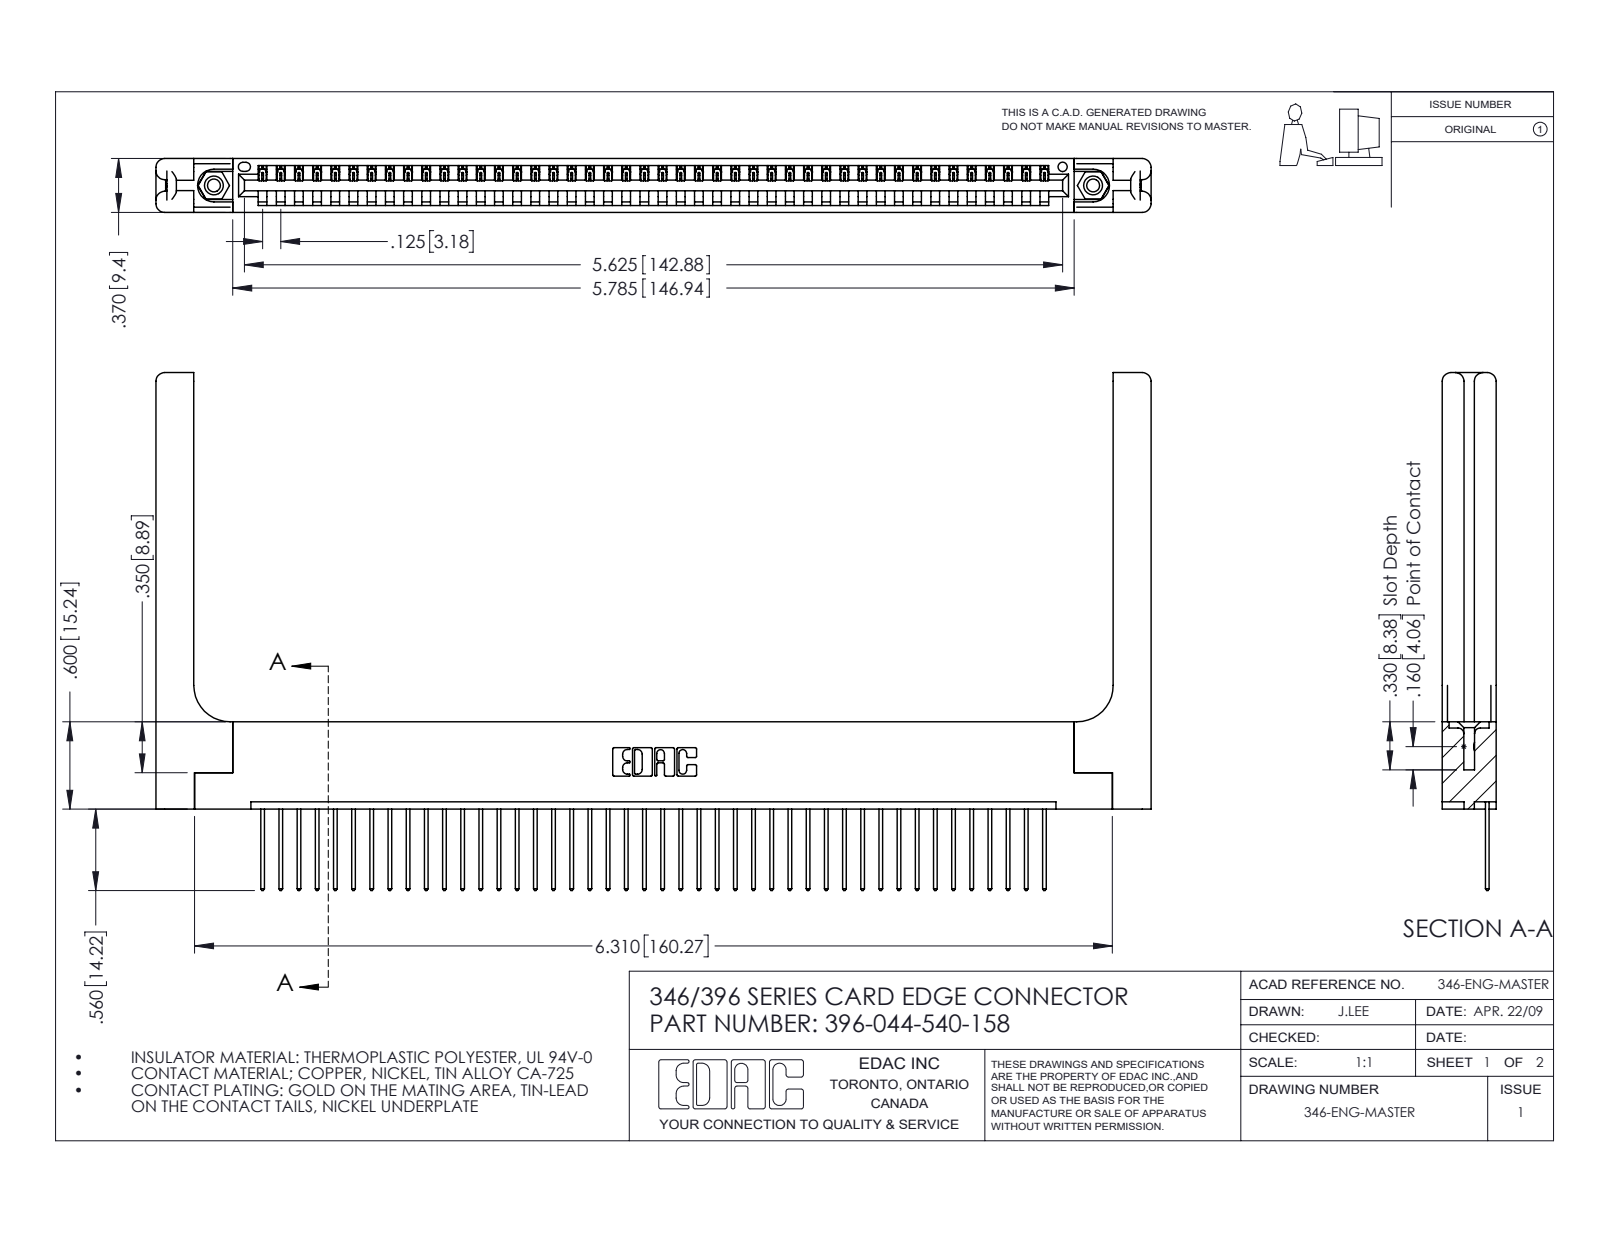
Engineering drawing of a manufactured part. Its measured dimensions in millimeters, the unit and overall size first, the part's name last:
Units: millimetres
Overall size (bounding box): 173.8 × 90.4 × 9.4
Round holes (diameter × count): ⌀2.3 ×2, ⌀3.2 ×2, ⌀4 ×2, ⌀1.6 ×1
Round bosses / shafts (diameter × count): ⌀3.9 ×2
Partial cylindrical surfaces — rounded edges, fillets, slot ends (radius × count): R0.2 ×88, R0.3 ×88, R0.3 ×22, R1.5 ×16, R0.2 ×6, R0.8 ×6, R0.7 ×3, R0.8 ×2
Main face-to-face distances: 9.4, 1.2, 8.2, 1.8, 3.8, 3.8, 6.4, 7.6, 0.6, 5.6
Hole centre spacings: 6.2, 148.2, 153.5
Volume: 24 220 mm³ · Surface area: 26 510 mm²
Bodies: 49 solids, 2930 faces (1984 planar, 886 cylindrical, 60 other)
Part name (STEP PRODUCT): 346 Part_Flush Mounting Lugs - 0.156 Dia-TH; 346-220-058_345-220-058; 345-292-001_345-293-140; 396-044-540-158 (+1 more)
STEP written by: SolidWorks 2016 (CONFIG_CONTROL_DESIGN)
